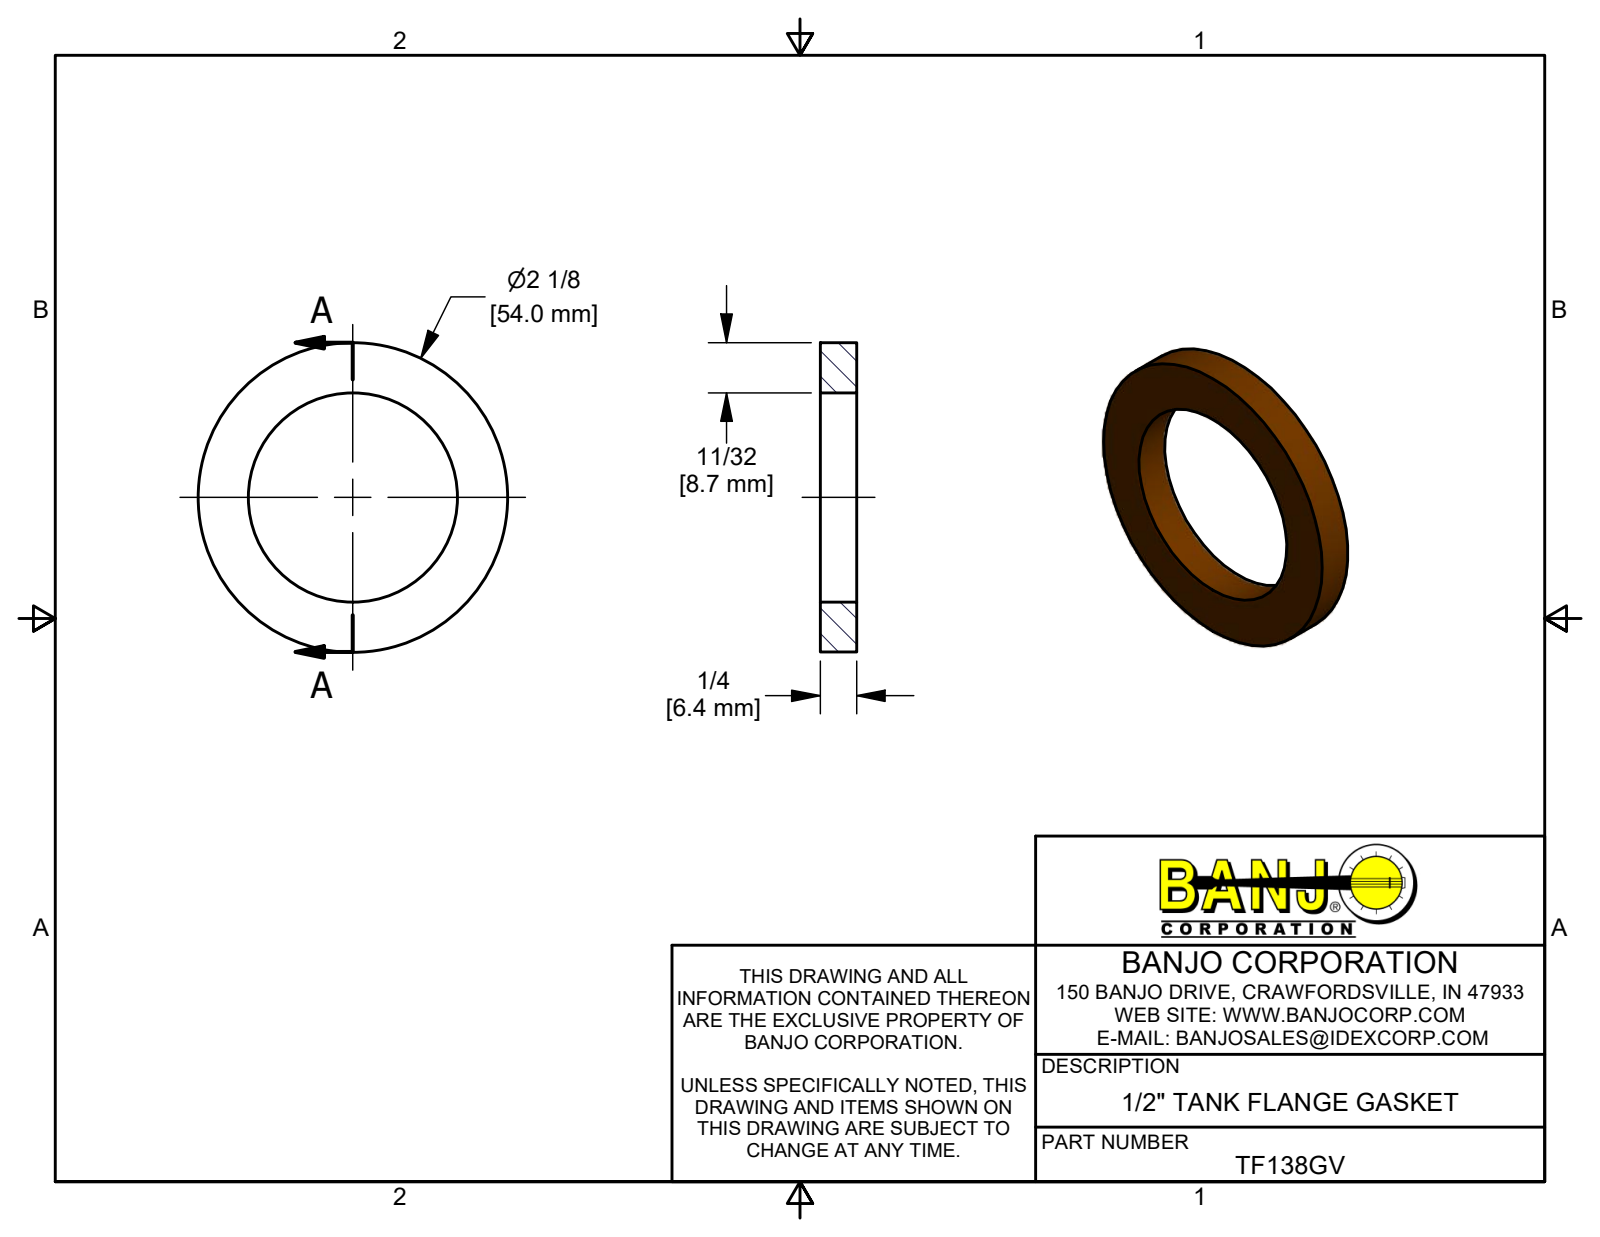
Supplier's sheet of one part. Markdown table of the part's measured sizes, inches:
| quantity | value |
| --- | --- |
| part name | TF138GV |
| STEP written by | Autodesk Inventor 2019 (AUTOMOTIVE_DESIGN) |
| units | inches |
| bodies | 1 solid, 4 faces (2 planar, 2 cylindrical, 0 other) |
| overall size | 2.125 × 2.125 × 0.25 |
| volume | 0.481 in³ |
| surface area | 6.645 in² |
| round holes (diameter × count) | 1.437 × 1 |
| round bosses / shafts (diameter × count) | 2.125 × 1 |
| main face-to-face distances | 0.25 |
